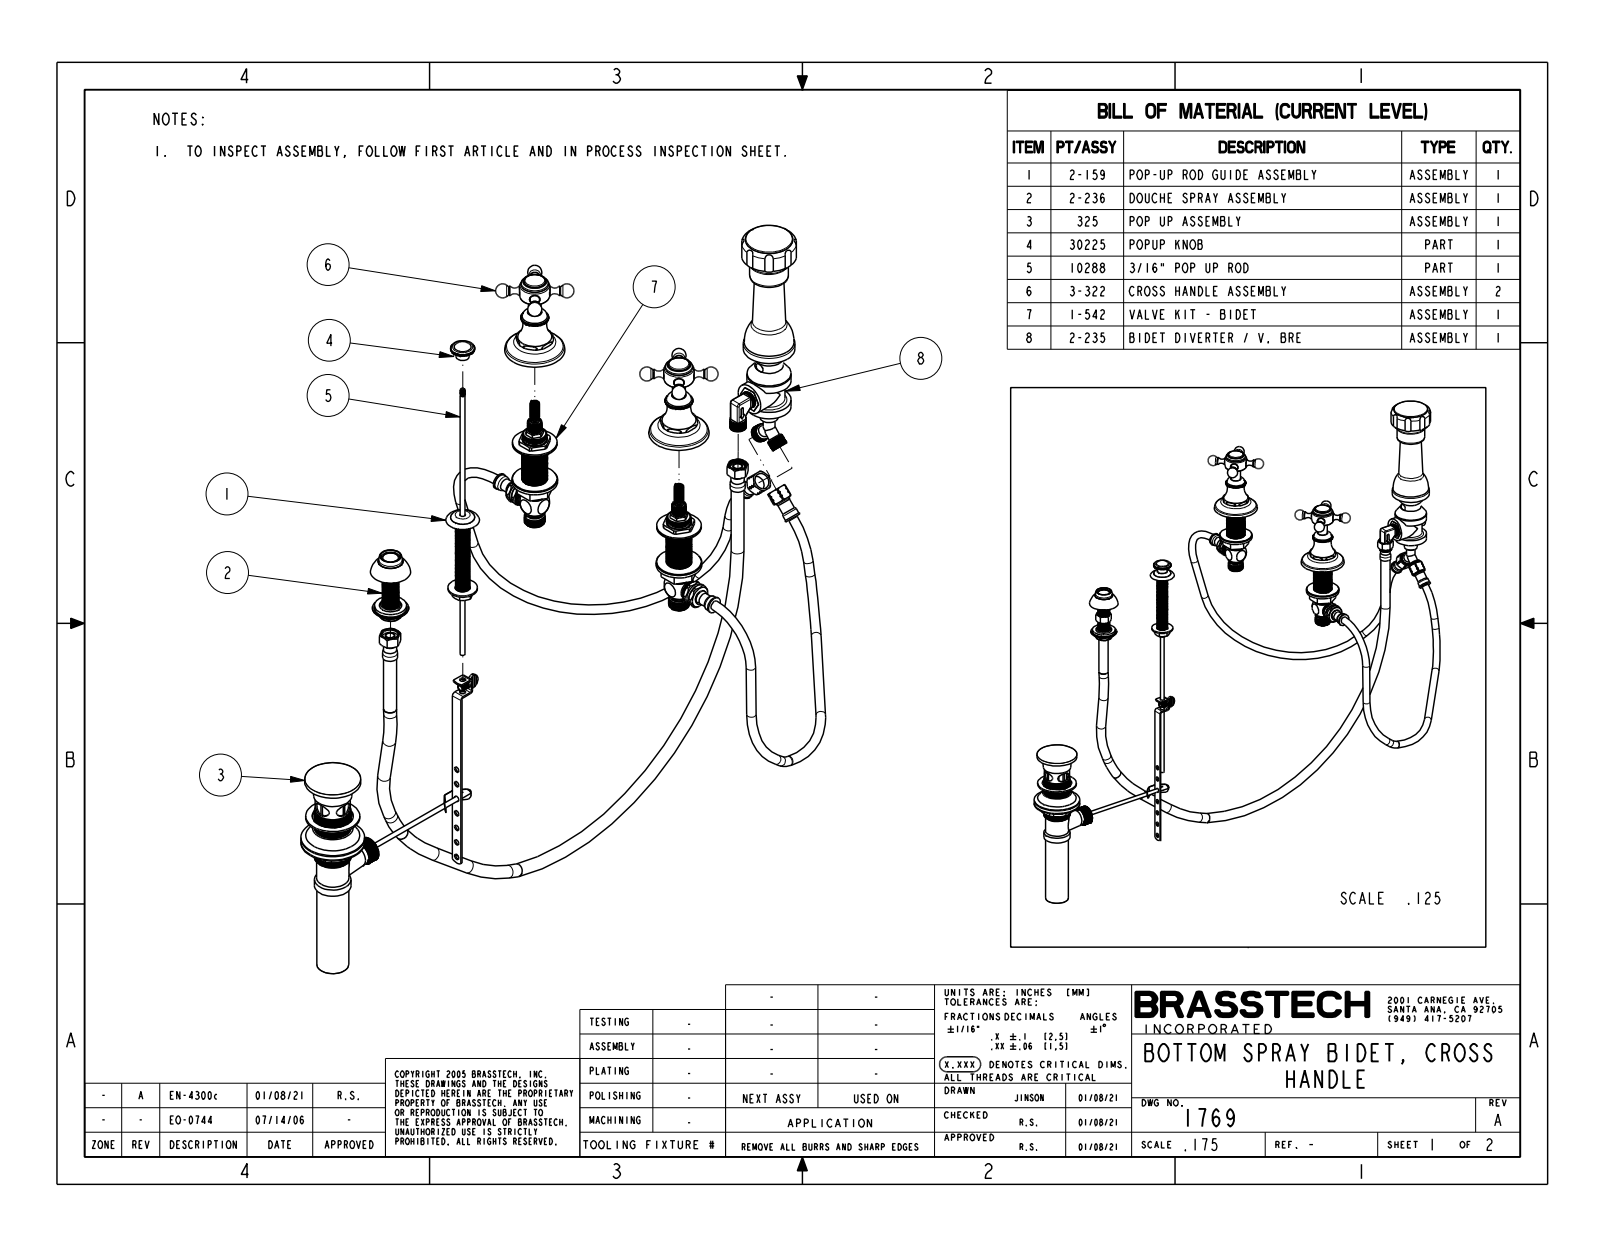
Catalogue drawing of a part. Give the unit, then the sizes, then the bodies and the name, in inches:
Units: inches
Overall size (bounding box): 22.855 × 10.365 × 5.353
Round holes (diameter × count): ⌀0.41 ×8, ⌀0.855 ×2, ⌀0.625 ×1, ⌀0.792 ×1, ⌀0.94 ×1
Round bosses / shafts (diameter × count): ⌀0.392 ×8, ⌀0.84 ×2, ⌀0.5 ×2, ⌀2.025 ×1, ⌀1.52 ×1, ⌀0.925 ×1, ⌀0.775 ×1
Partial cylindrical surfaces — rounded edges, fillets, slot ends (radius × count): R0.21 ×8, R0.357 ×1, R1.077 ×1
Main face-to-face distances: 2.54, 3.468, 0.928, 1.375, 0.674, 1.866, 2.794, 4, 5.228, 4.554
Hole centre spacings: 5.657, 12.649, 8
Volume: 20.46 in³ · Surface area: 99.12 in²
Bodies: 5 solids, 785 faces (481 planar, 82 cylindrical, 222 other)
Part name (STEP PRODUCT): 1769
STEP written by: CREO PARAMETRIC BY PTC INC, 2018400 (CONFIG_CONTROL_DESIGN)
